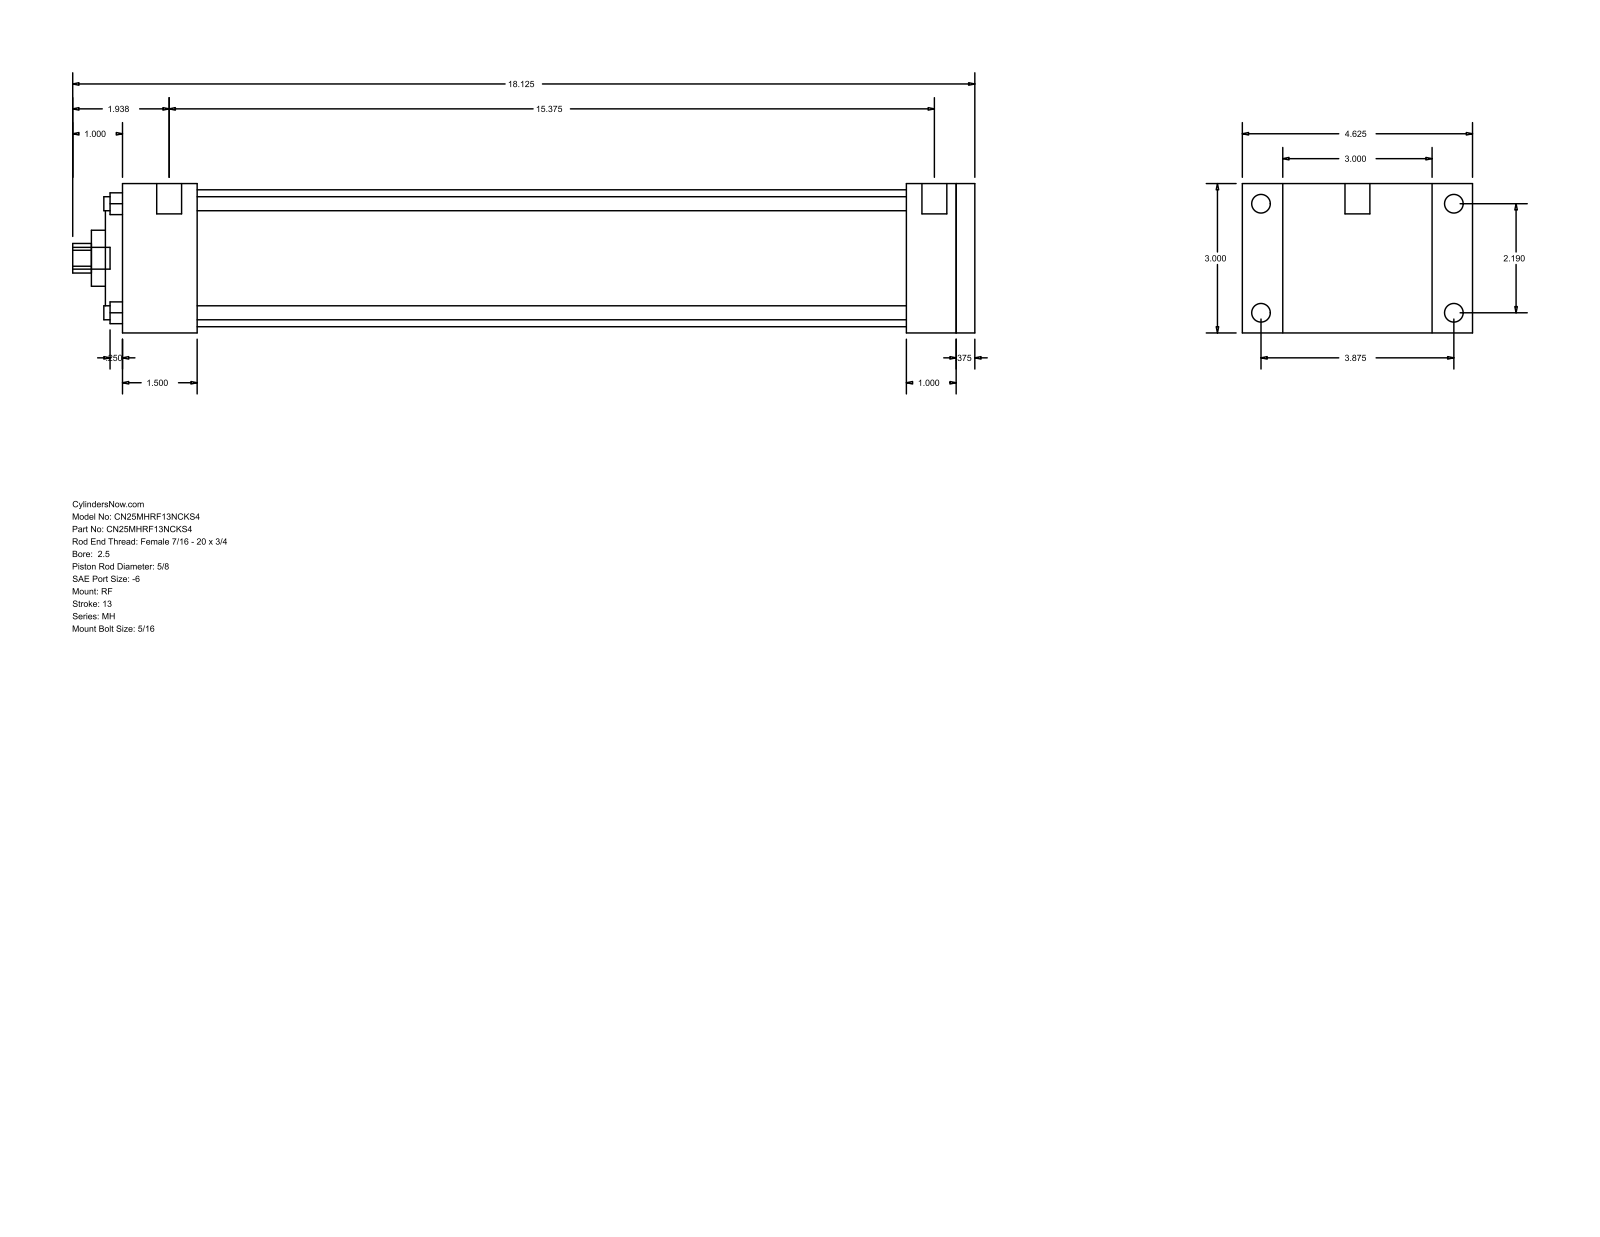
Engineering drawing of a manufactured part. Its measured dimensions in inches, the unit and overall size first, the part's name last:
Units: inches
Overall size (bounding box): 18.125 × 4.625 × 3
Round holes (diameter × count): ⌀0.281 ×4, ⌀0.625 ×1, ⌀1.125 ×1, ⌀2.187 ×1, ⌀2.75 ×1
Round bosses / shafts (diameter × count): ⌀0.375 ×4, ⌀0.219 ×4, ⌀0.5 ×2, ⌀0.437 ×1
Partial cylindrical surfaces — rounded edges, fillets, slot ends (radius × count): R0.297 ×1
Main face-to-face distances: 3, 0.375, 17.125, 16.75, 1, 15.75, 1.375, 1.5, 14.25, 15.25
Hole centre spacings: 1.548, 2.19, 3.097
Bodies: 0 solids, 94 faces (65 planar, 29 cylindrical, 0 other)
Part name (STEP PRODUCT): MH_RF__0250_0.625
STEP written by: GSSL Pune (CONFIG_CONTROL_DESIGN)
